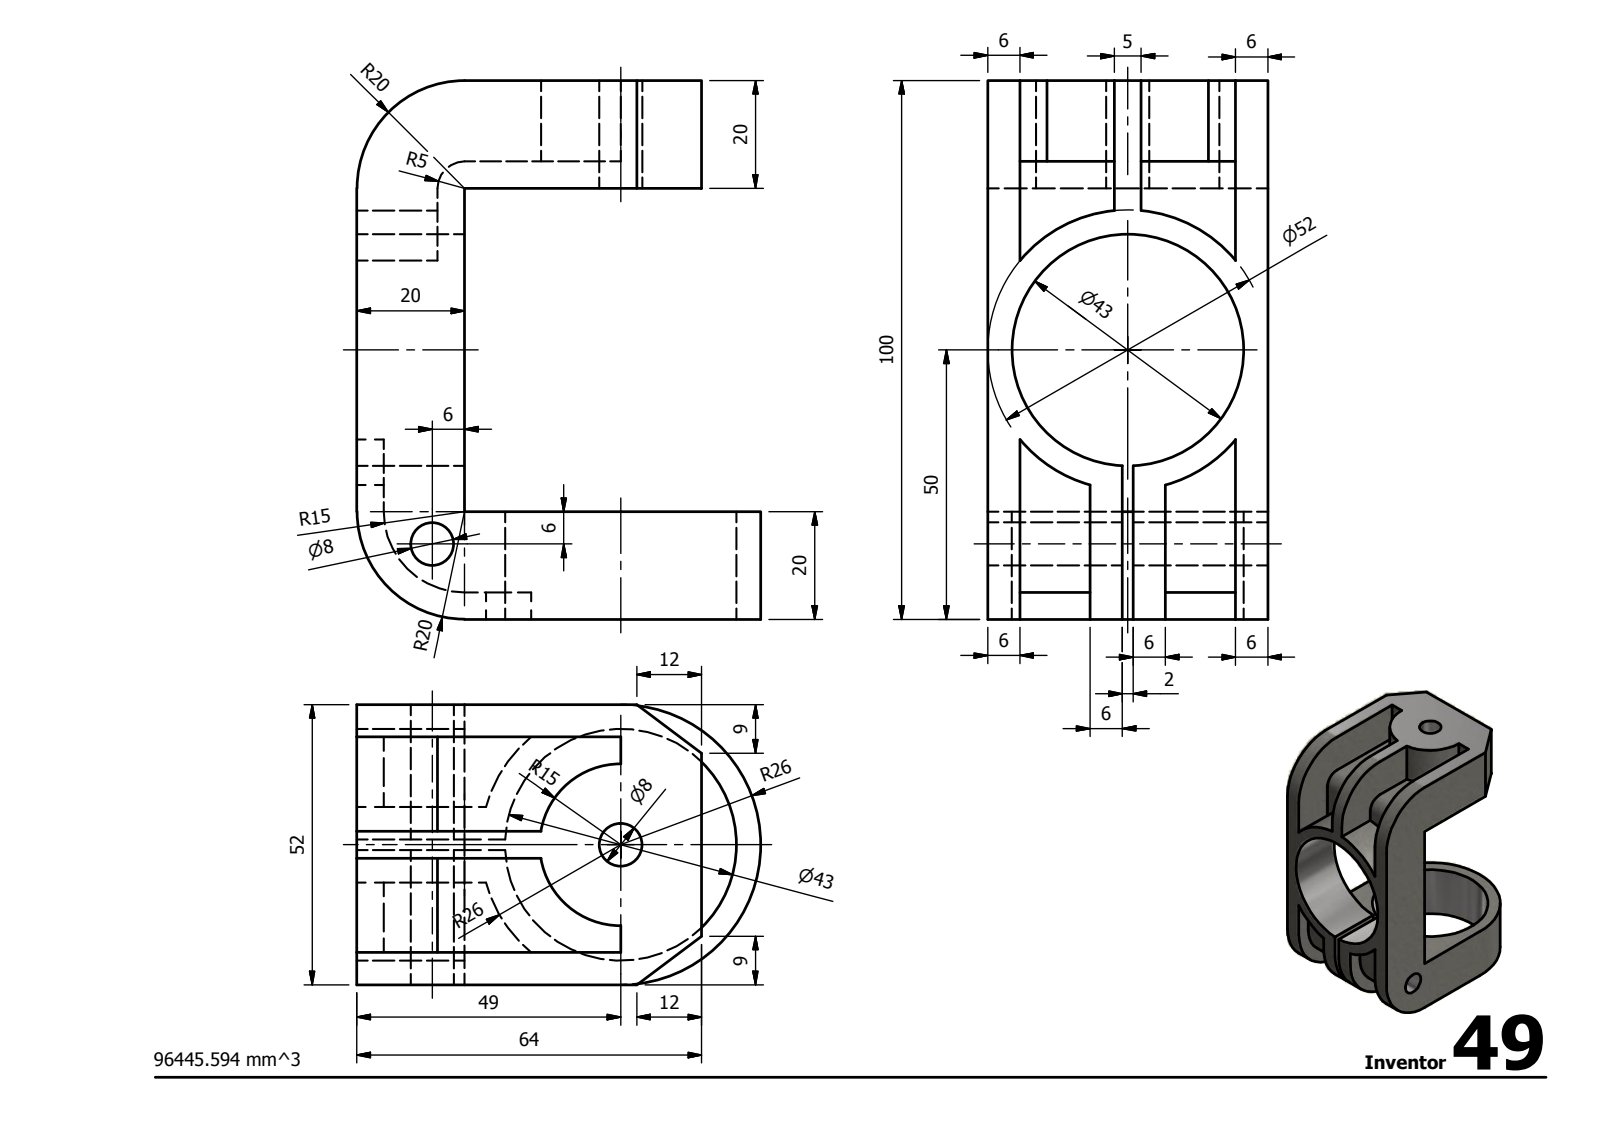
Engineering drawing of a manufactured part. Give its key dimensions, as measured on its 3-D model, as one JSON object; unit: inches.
{"step_written_by": "Autodesk Inventor 2014 (AUTOMOTIVE_DESIGN)", "units": "inches", "bodies": {"solids": 1, "faces": 56, "planar": 31, "cylindrical": 25, "other": 0}, "overall_size": [3.937, 2.953, 2.047], "volume_in3": 5.885, "surface_area_in2": 53.79, "round_holes": [[0.315, 2], [1.693, 2]], "partial_cylinders_radius": [[0.591, 2], [0.787, 2], [1.024, 2], [0.197, 1]], "face_to_face_distances": [0.787, 2.047, 0.236, 1.811, 3.15, 0.197, 0.591, 0.748, 1.063, 1.575]}
